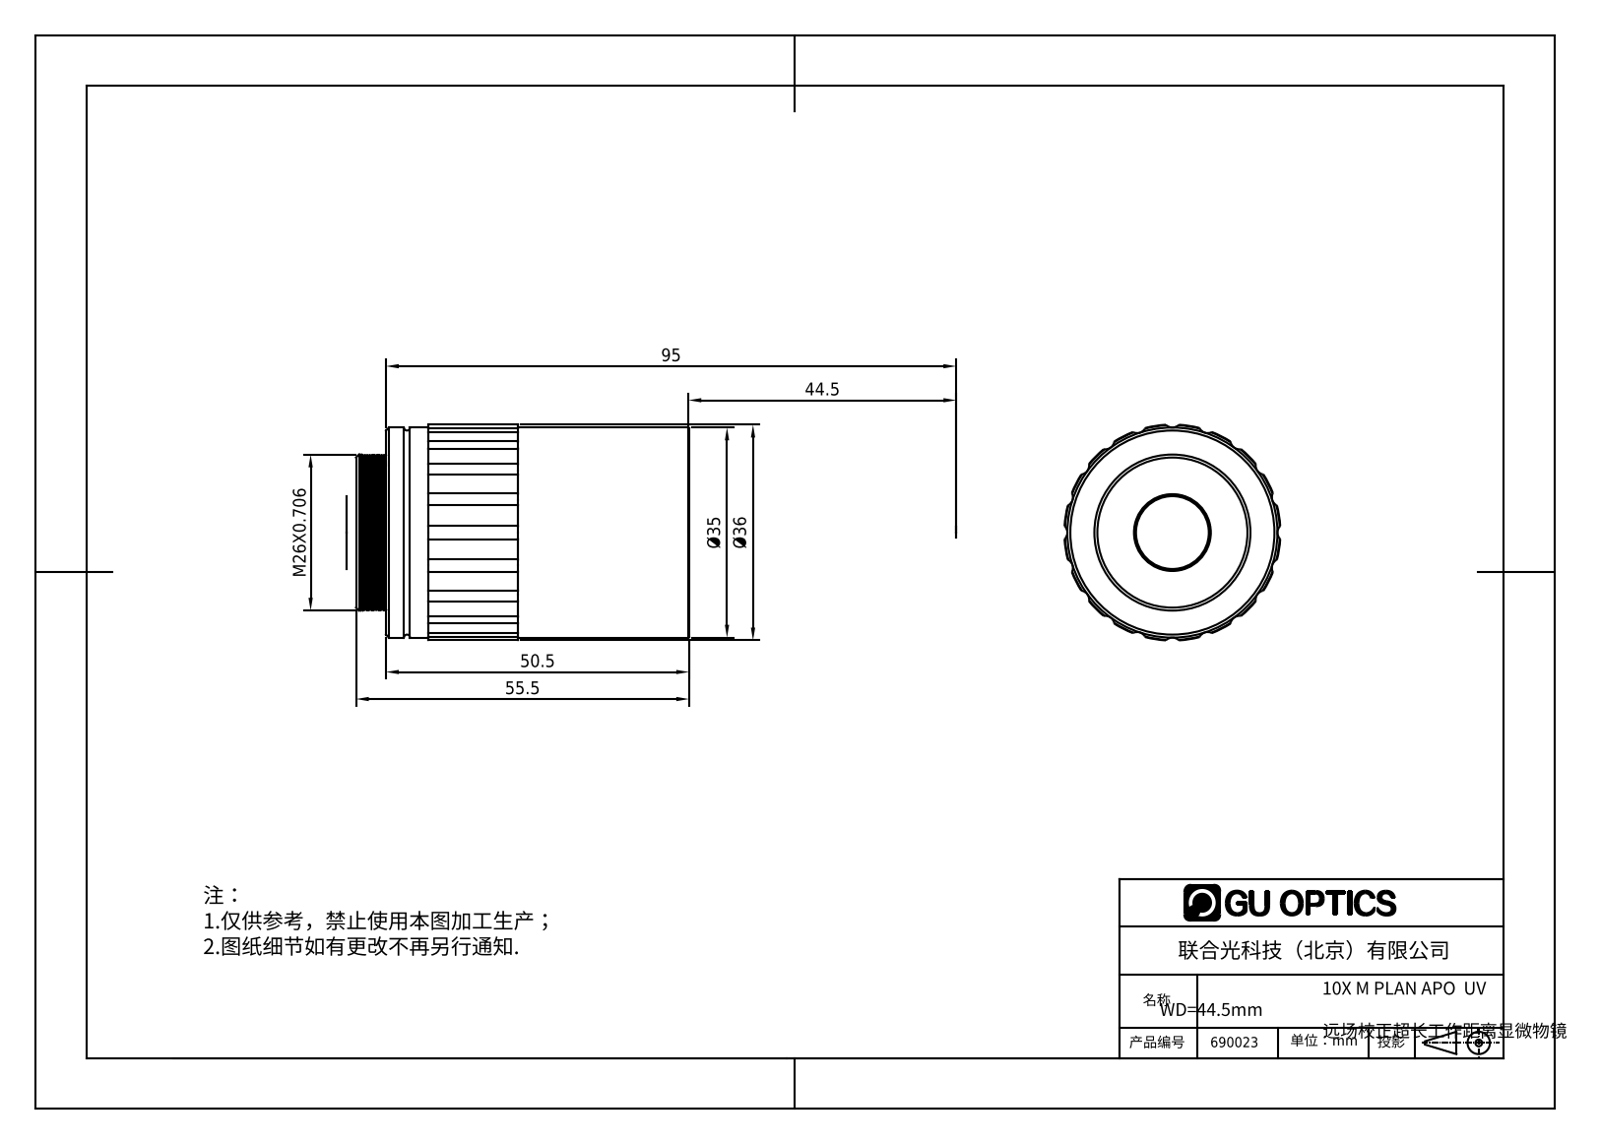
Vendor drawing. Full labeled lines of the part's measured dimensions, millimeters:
Part name (STEP PRODUCT): 10x 物镜展示
STEP written by: SolidWorks 2020 (CONFIG_CONTROL_DESIGN)
Units: millimetres
Bodies: 18 solids, 271 faces (87 planar, 79 cylindrical, 105 other)
Overall size (bounding box): 101.51 × 35.93 × 35.93
Volume: 34 943 mm³ · Surface area: 28 684 mm²
Round holes (diameter × count): ⌀12.6 ×1, ⌀14 ×1, ⌀14.63 ×1, ⌀24.4 ×1, ⌀25 ×1, ⌀27.6 ×1, ⌀29.8 ×1, ⌀30 ×1, ⌀30.6 ×1, ⌀32 ×1, ⌀33 ×1, ⌀33.4 ×1
Round bosses / shafts (diameter × count): ⌀35 ×1, ⌀34 ×1, ⌀31.8 ×1, ⌀26.4 ×1, ⌀26 ×1, ⌀21 ×1, ⌀13.6 ×1, ⌀12.4 ×1
Partial cylindrical surfaces — rounded edges, fillets, slot ends (radius × count): R1.5 ×20, R18 ×1
Main face-to-face distances: 43.69, 5.45, 49.14, 0.86, 6.31, 50, 5, 5.86, 11.31, 55
